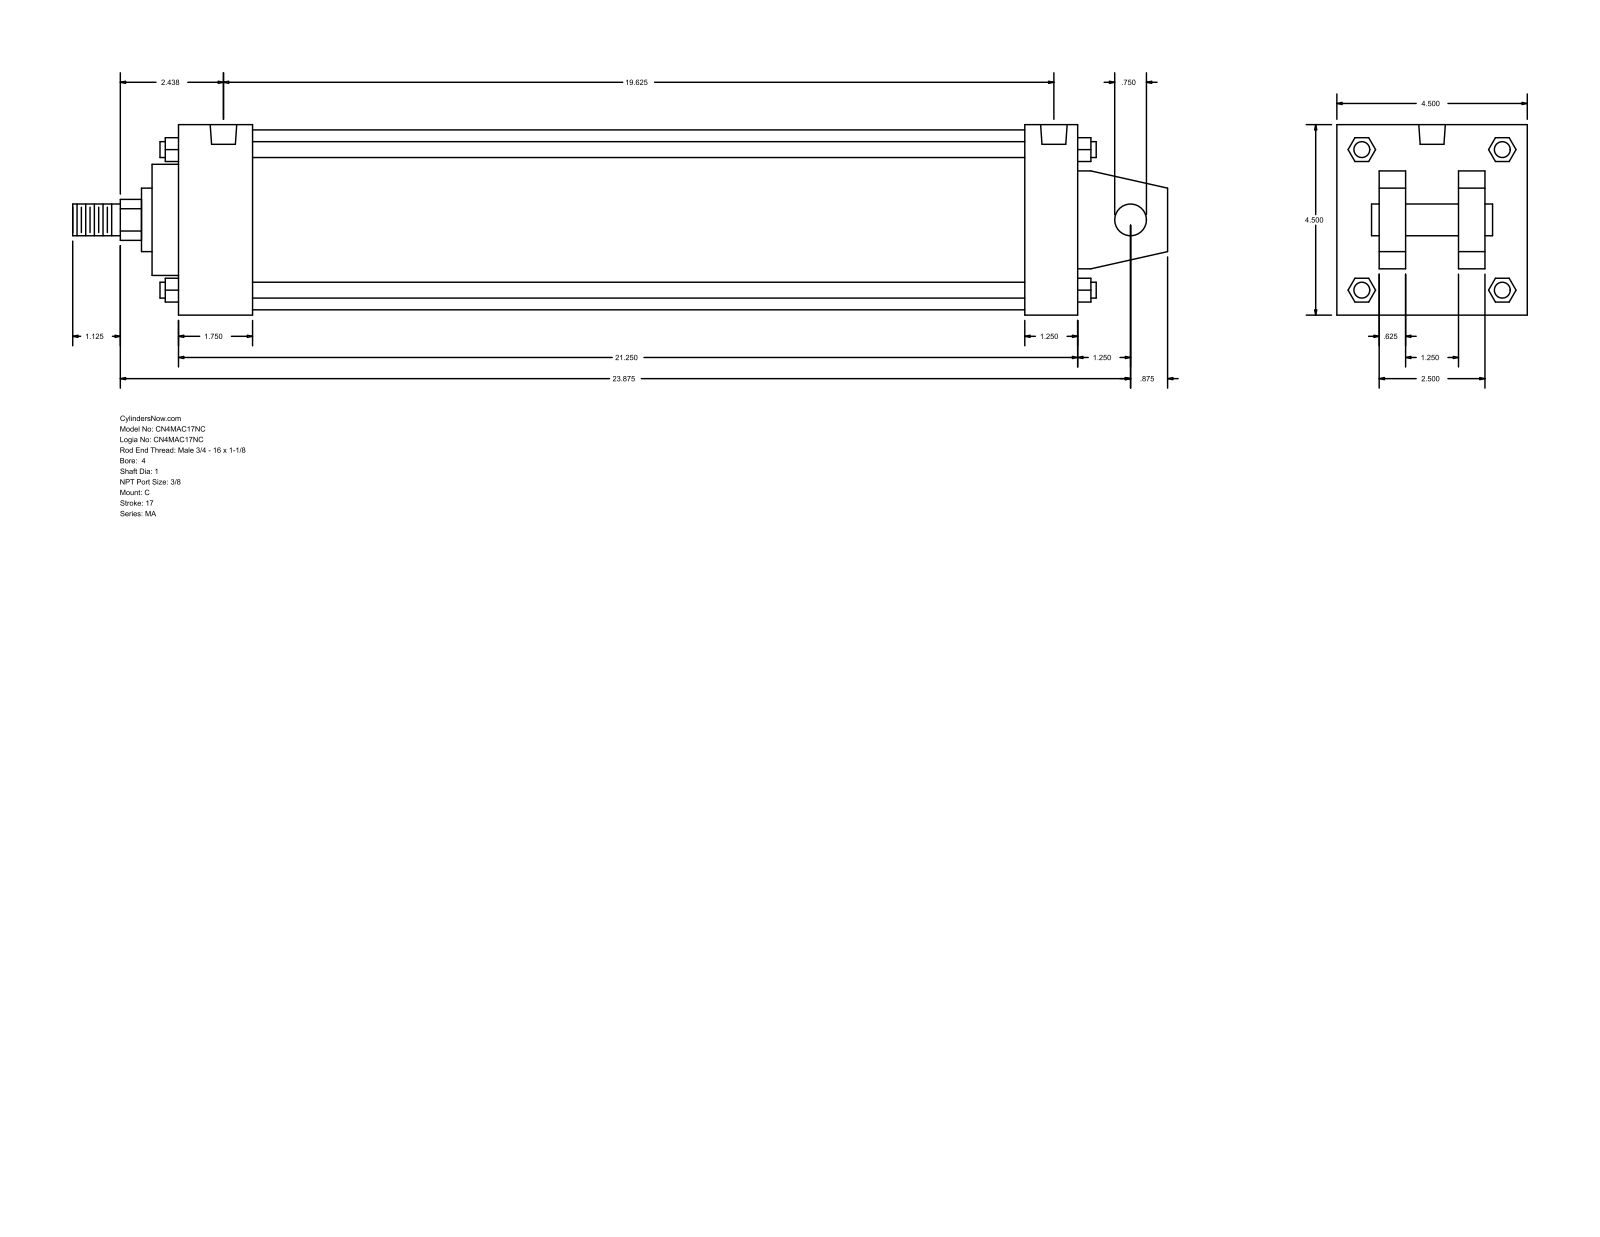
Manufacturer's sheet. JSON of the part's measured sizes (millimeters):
{"part_name": "MA_C__0400_1", "step_written_by": "GSSL Pune (CONFIG_CONTROL_DESIGN)", "units": "millimeters", "bodies": {"solids": 0, "faces": 141, "planar": 109, "cylindrical": 32, "other": 0}, "overall_size": [657.23, 114.3, 114.3], "round_holes": [[11.11, 4], [15.93, 2]], "round_bosses_or_shafts": [[9.53, 4], [19.05, 2], [107.95, 1], [66.67, 1], [38.1, 1], [25.4, 1]], "partial_cylinders_radius": [[12.29, 1]], "face_to_face_distances": [114.3, 539.75, 15.87, 73.03, 41.27, 25.4, 88.9, 47.63, 508, 31.75], "hole_center_spacings": [488.95, 4.76, 4.77, 493.71, 493.72, 498.48]}
